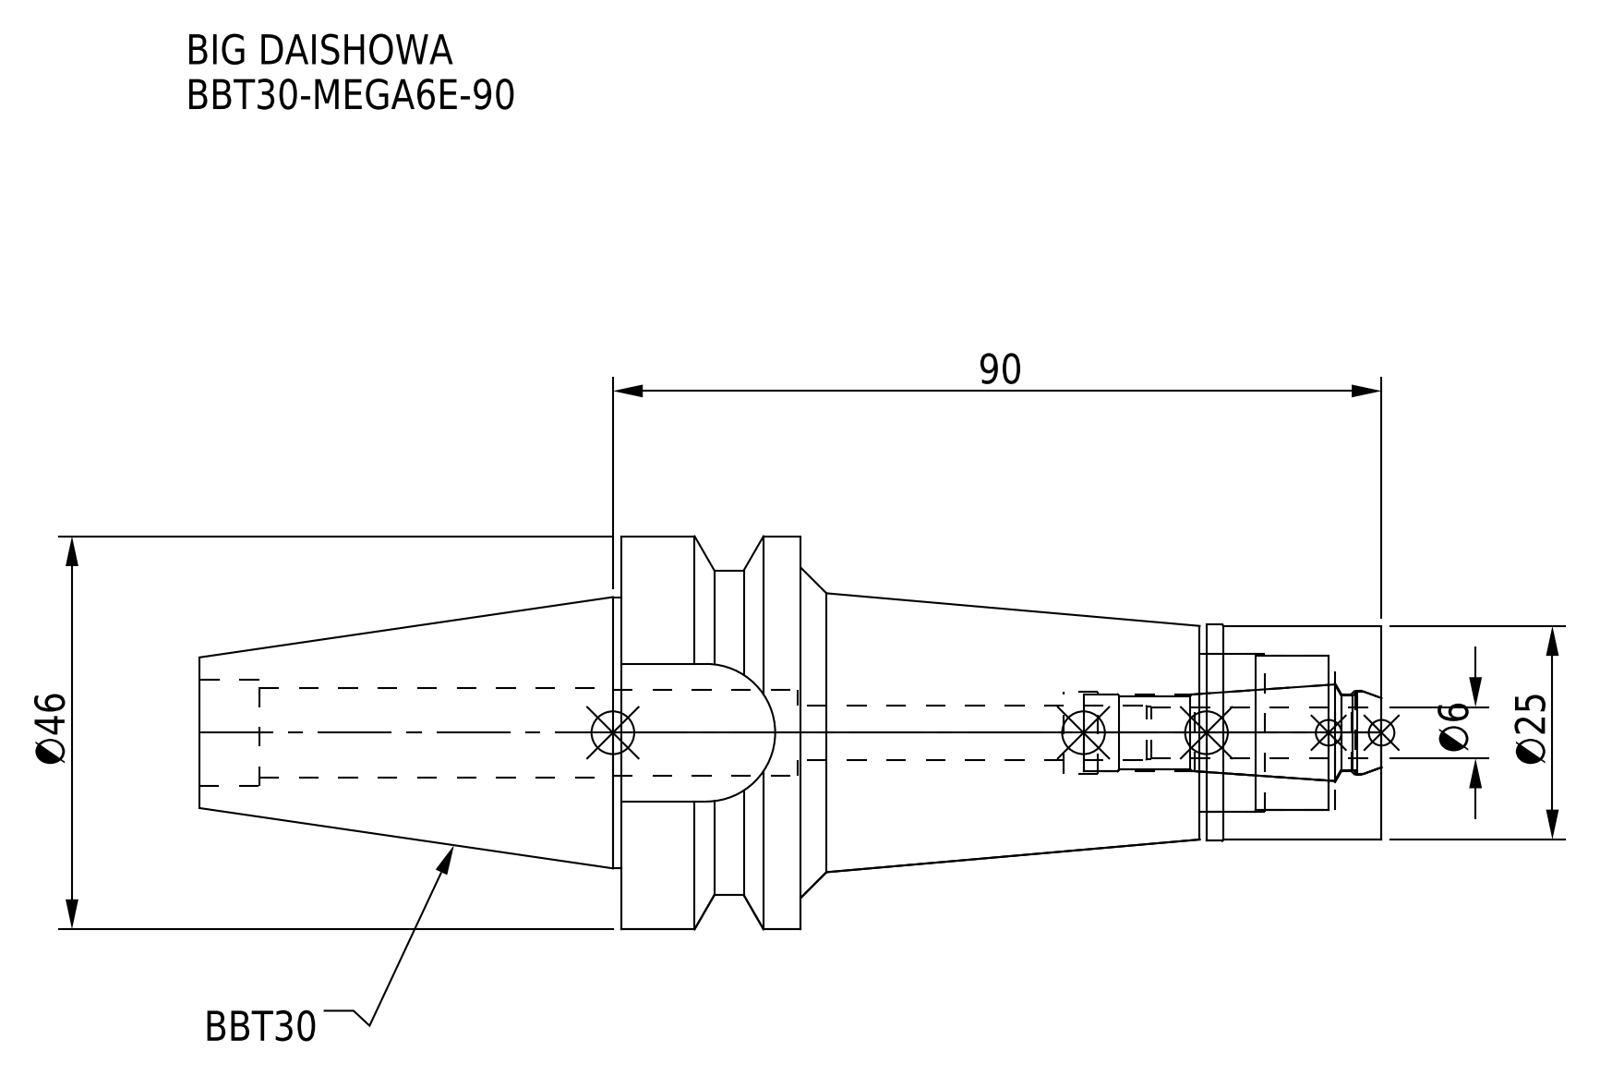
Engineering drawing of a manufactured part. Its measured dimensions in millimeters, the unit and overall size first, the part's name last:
Units: millimetres
Overall size (bounding box): 138.4 × 46 × 46
Round holes (diameter × count): ⌀6.4 ×1, ⌀9 ×1, ⌀9.6 ×1, ⌀9.9 ×1, ⌀10 ×1, ⌀10.4 ×1, ⌀12.5 ×1, ⌀18 ×1, ⌀18.5 ×1
Round bosses / shafts (diameter × count): ⌀46 ×1, ⌀31.75 ×1, ⌀25.3 ×1, ⌀25 ×1
Partial cylindrical surfaces — rounded edges, fillets, slot ends (radius × count): R8.05 ×1, R19 ×1
Main face-to-face distances: 21, 68, 89, 32.6, 20.5, 47.5, 68.5, 21.3, 0.8, 46.7
Volume: 85 894 mm³ · Surface area: 22 157 mm²
Bodies: 2 solids, 79 faces (21 planar, 38 cylindrical, 20 other)
Part name (STEP PRODUCT): BBT30-MEGA6E-90-060.stp; MEN6_1.stp; BBT30-MEGA6E-90_1.stp; DXF_TEMP_ASSY_ASM_4_ASM.stp (+3 more)
STEP written by: SolidWorks 2019 (CONFIG_CONTROL_DESIGN)
